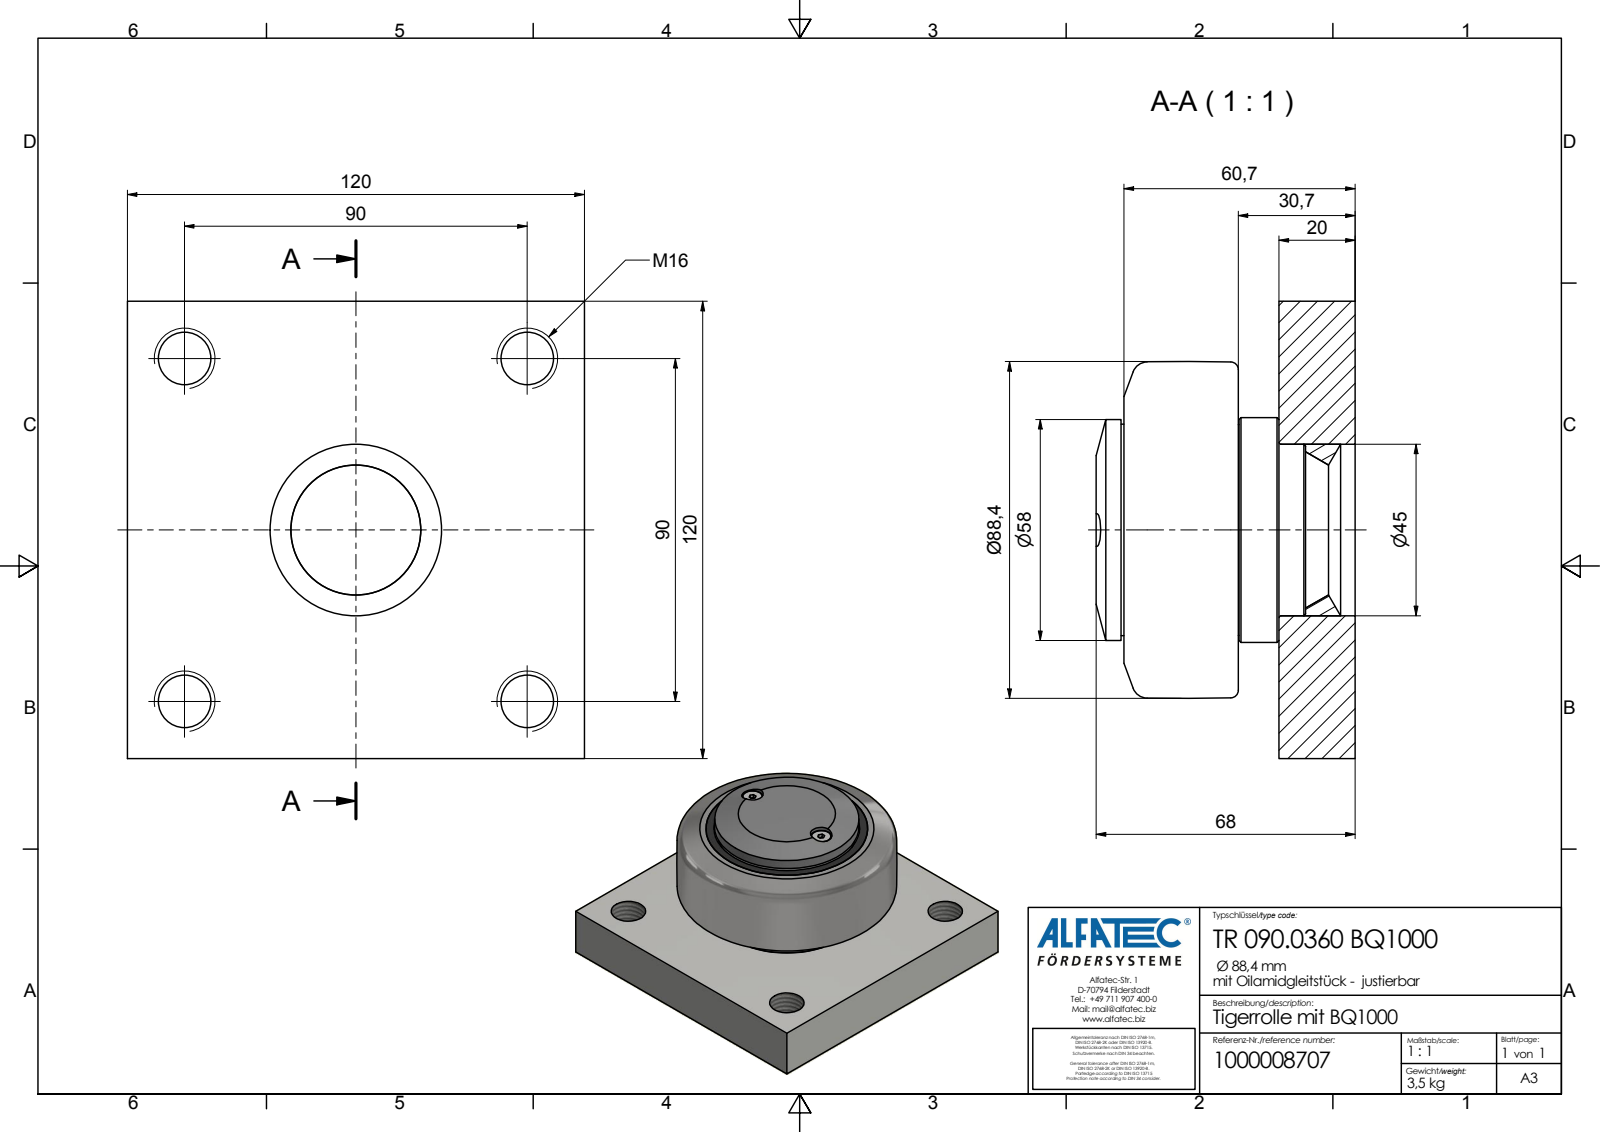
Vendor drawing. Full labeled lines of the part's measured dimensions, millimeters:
Part name (STEP PRODUCT): TR 090.0360 BQ1000_Kontur
STEP written by: Autodesk Inventor 2020 (AP242_MANAGED_MODEL_BASED_3D_ENGINEERING_MIM_LF)
Units: millimetres
Bodies: 1 solid, 51 faces (28 planar, 13 cylindrical, 10 other)
Overall size (bounding box): 120 × 120 × 68
Volume: 491 327 mm³ · Surface area: 59 382 mm²
Round holes (diameter × count): ⌀13.84 ×4, ⌀8.6 ×2, ⌀45 ×1
Round bosses / shafts (diameter × count): ⌀7.8 ×2, ⌀59 ×1, ⌀58 ×1, ⌀55.5 ×1, ⌀55.3 ×1
Main face-to-face distances: 20, 120, 30.7, 10.7, 60.7, 40.7, 30, 68, 48, 37.3
Hole centre spacings: 51.72, 63.64, 78.65, 90, 19.5, 127.28, 39
